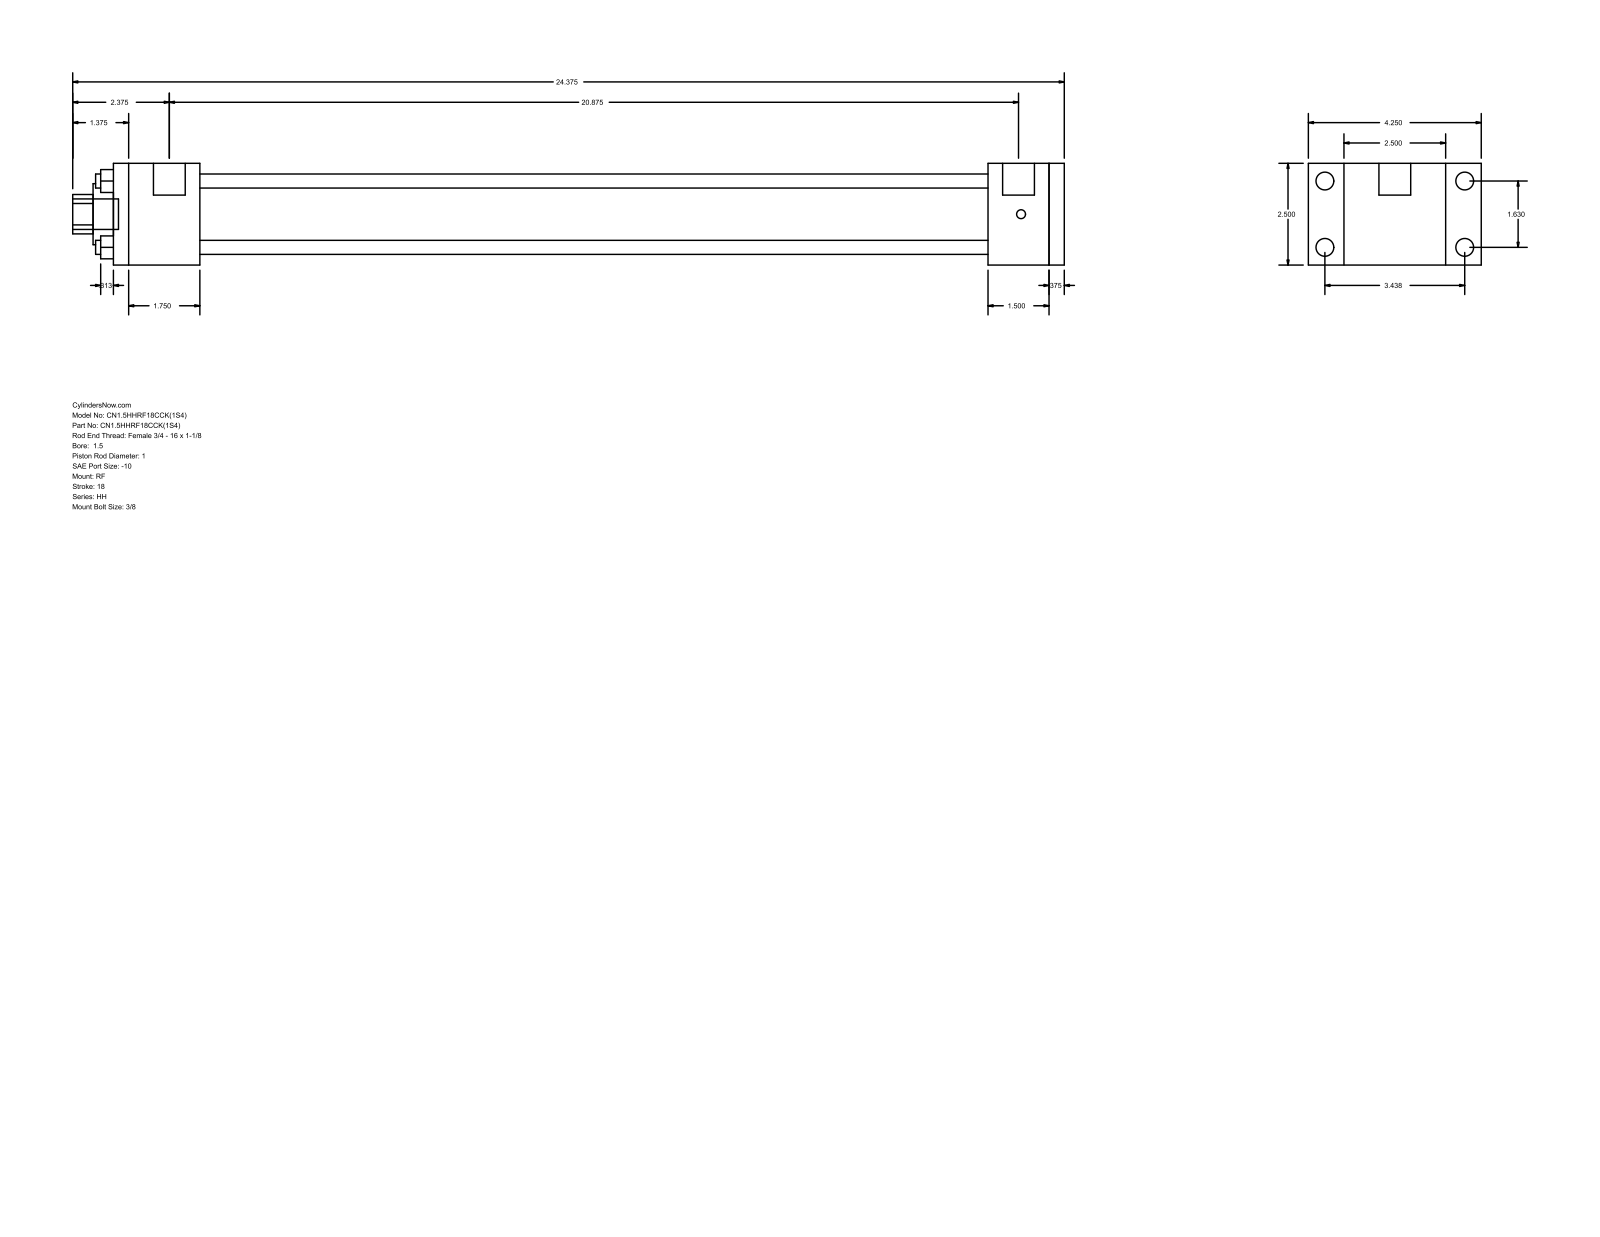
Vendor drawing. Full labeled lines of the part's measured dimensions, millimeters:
Part name (STEP PRODUCT): HH_RF__0150_1
STEP written by: GSSL Pune (CONFIG_CONTROL_DESIGN)
Units: millimetres
Bodies: 0 solids, 92 faces (64 planar, 28 cylindrical, 0 other)
Overall size (bounding box): 619.12 × 107.95 × 63.5
Round holes (diameter × count): ⌀8.76 ×4, ⌀25.4 ×1, ⌀38.1 ×1, ⌀44.45 ×1
Round bosses / shafts (diameter × count): ⌀11.13 ×4, ⌀5.56 ×4, ⌀19.84 ×2, ⌀19.05 ×1
Partial cylindrical surfaces — rounded edges, fillets, slot ends (radius × count): R12.29 ×1
Main face-to-face distances: 63.5, 9.52, 492.12, 530.22, 539.74, 38.1, 47.62, 53.98, 546.1, 584.2
Hole centre spacings: 29.27, 41.4, 58.55
